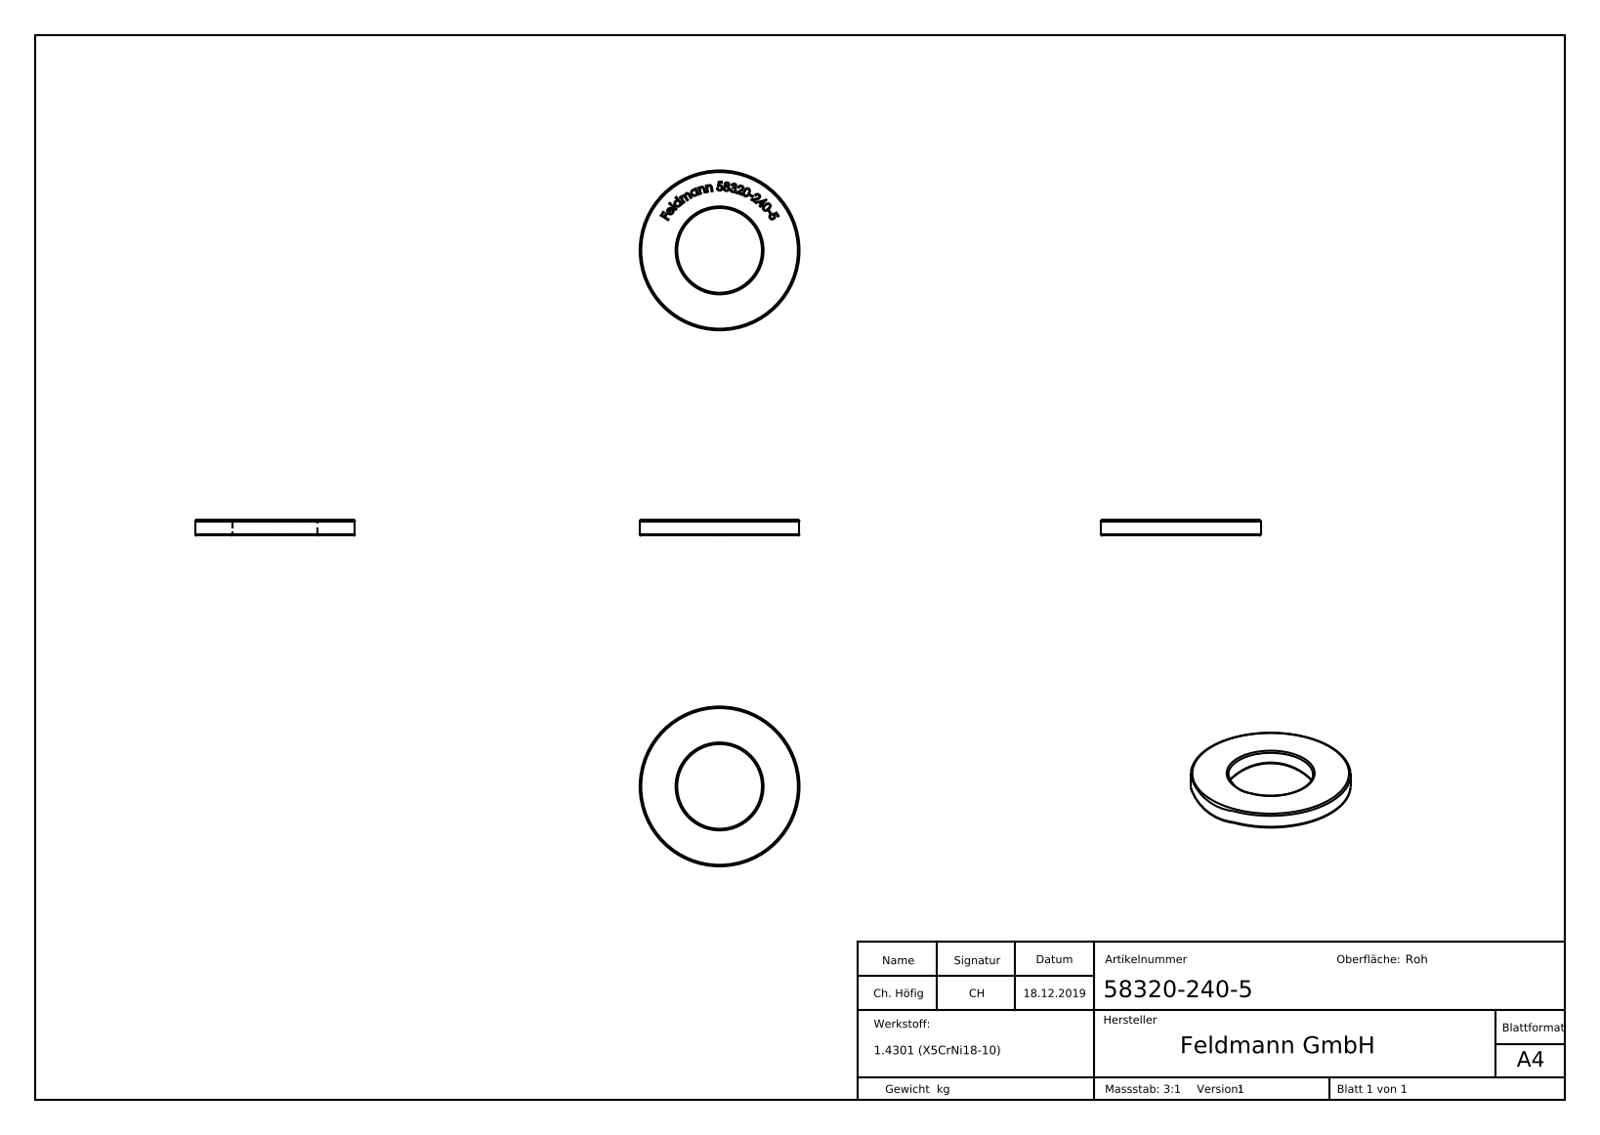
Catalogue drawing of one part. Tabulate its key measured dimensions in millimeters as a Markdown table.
| quantity | value |
| --- | --- |
| part name | 58320-240-5 |
| STEP written by | SolidWorks 2015 (CONFIG_CONTROL_DESIGN) |
| units | millimeters |
| bodies | 1 solid, 262 faces (131 planar, 2 cylindrical, 129 other) |
| overall size | 10 × 10 × 1 |
| volume | 56 mm³ |
| surface area | 161 mm² |
| round holes (diameter × count) | 5.3 × 1 |
| round bosses / shafts (diameter × count) | 10 × 1 |
| main face-to-face distances | 1, 0.9, 0.34, 0.53, 0.58, 0.31, 0.39, 0.32, 0.54, 0.35 |
